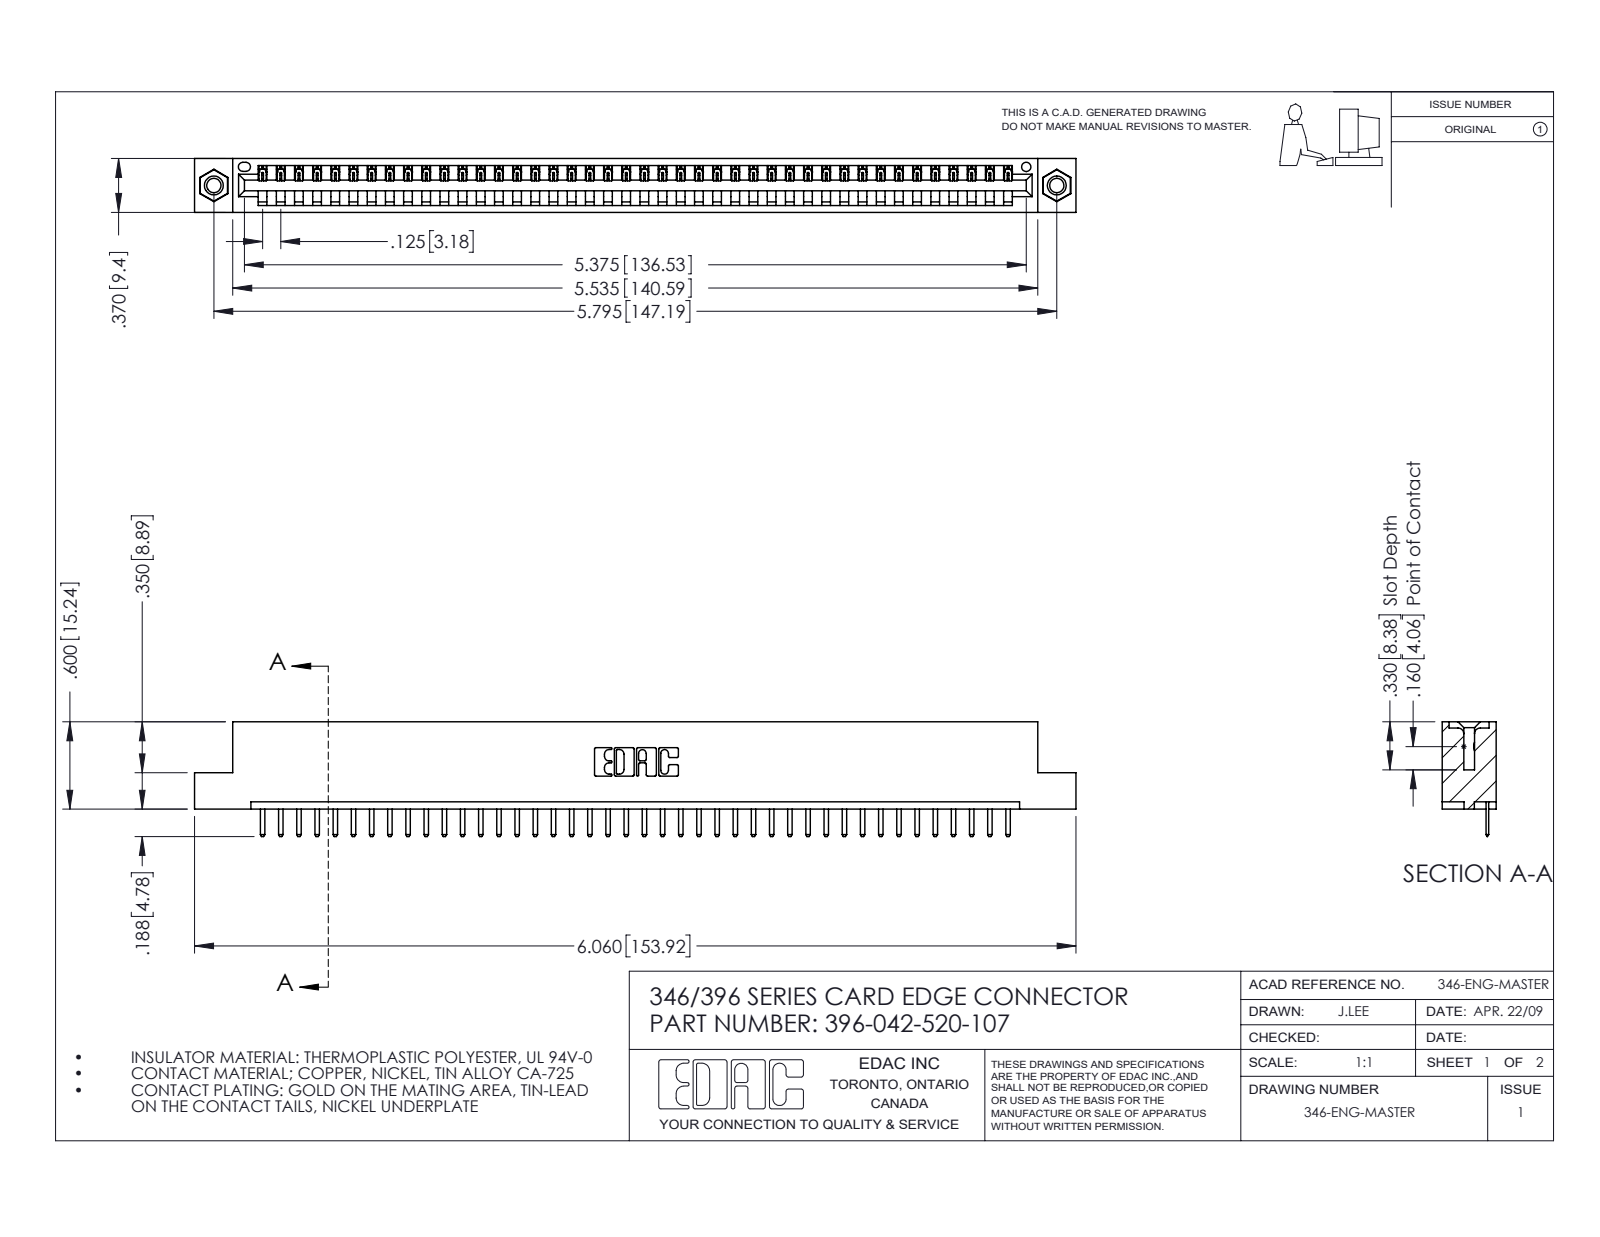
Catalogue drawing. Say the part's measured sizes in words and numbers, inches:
The part is named "396-042-520-107; 346 Part_Flush Mounting Lugs - 0.156 Dia-TI; 345-250-001_345-250-005-103; 345-292-001_345-293-120". Its 3-D file was written by "SolidWorks 2016 (CONFIG_CONTROL_DESIGN)". It is 45 solids with 2786 faces: 1872 planar, 898 cylindrical and 16 other. Overall it measures 6.06 by 0.788 by 0.37 inches. Its volume is 0.891 cubic inches and its surface area 27.71 square inches. Round holes: 2 of diameter 0.098, 2 of diameter 0.125, 2 of diameter 0.156, 1 of diameter 0.064. Round bosses or shafts: 2 of diameter 0.155. Partial cylindrical surfaces (rounded edges, fillets, slot ends): 86 of radius 0.01, 84 of radius 0.006, 22 of radius 0.01, 6 of radius 0.007, 6 of radius 0.031, 3 of radius 0.026, 2 of radius 0.031, 2 of radius 0.04. The main face-to-face distances are 0.048, 0.322, 0.37, 0.25, 0.148, 0.222, 0.1, 0.174, 0.072, 0.298. The hole center spacings are 0.246, 5.586, 5.795.
